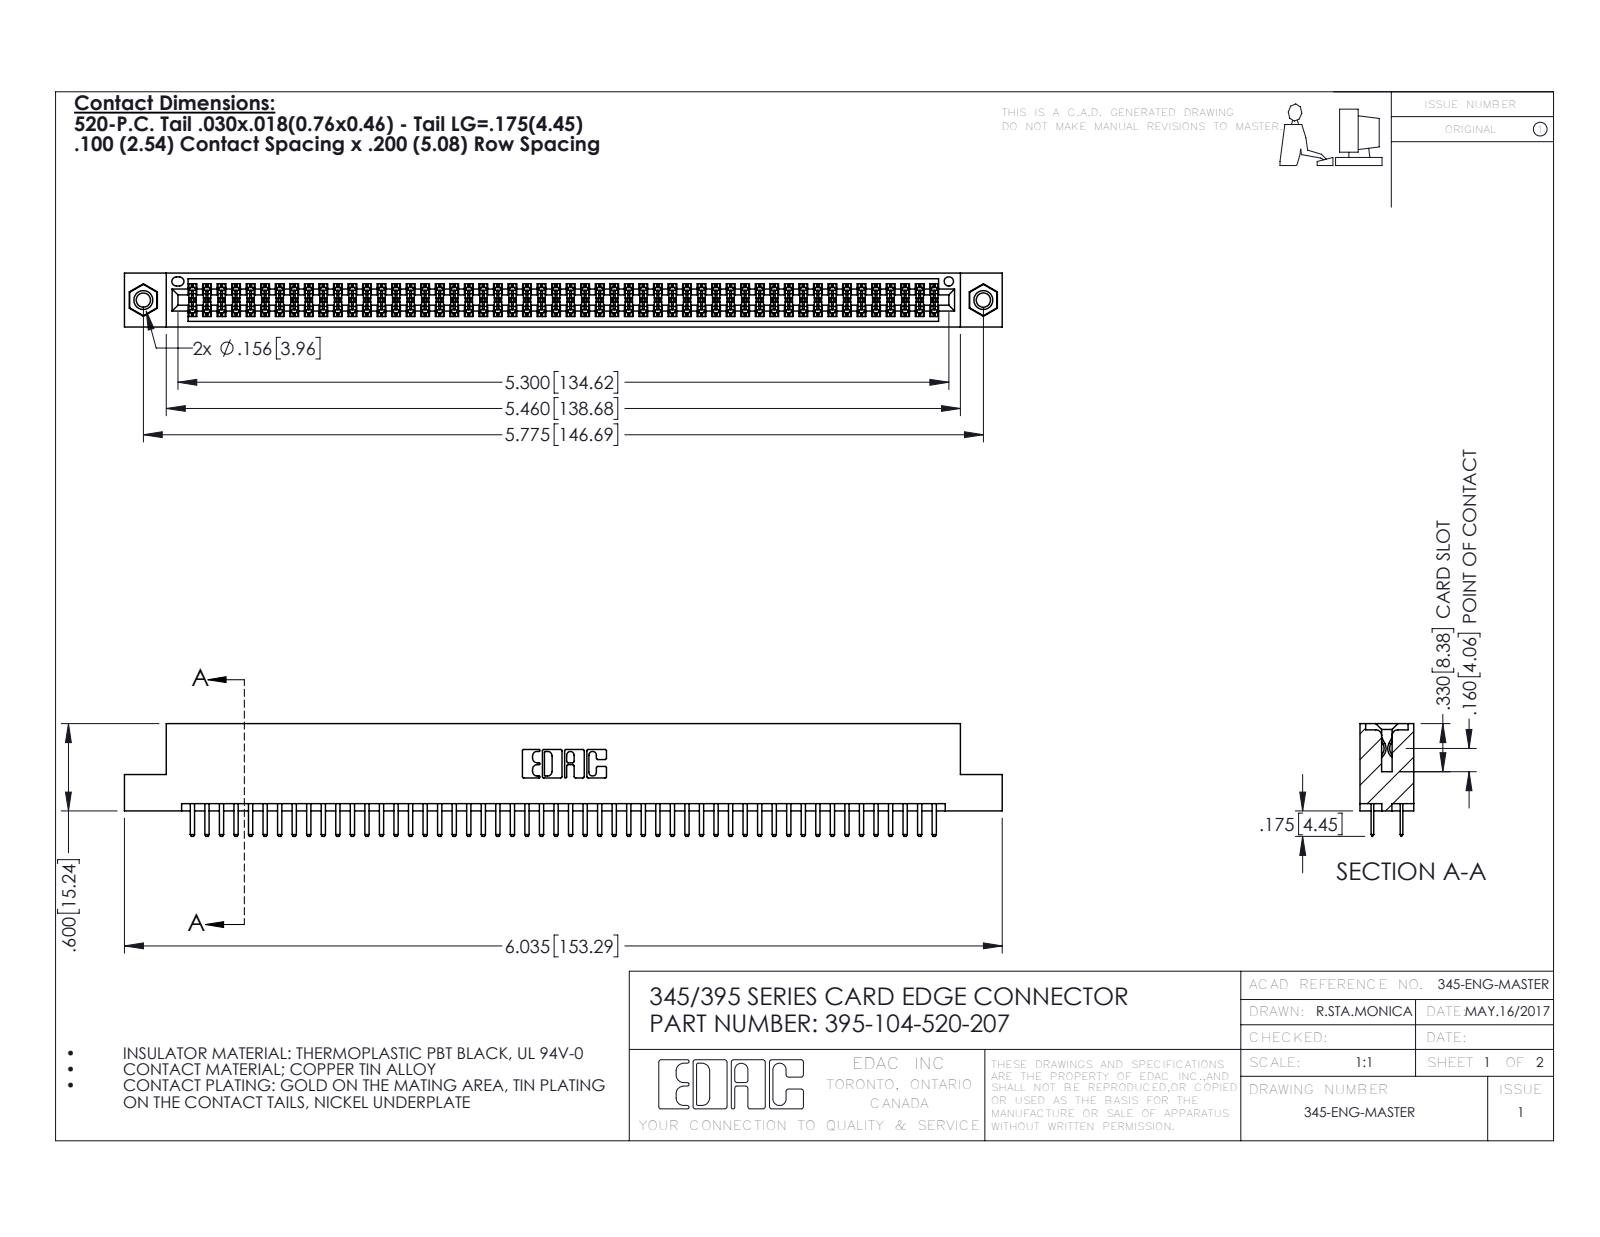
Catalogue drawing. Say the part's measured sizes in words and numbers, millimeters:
The part is named "345-292-001_345-293-120; 395-104-520-207; 345-250-001_345-250-005-103; 345 Part_Flush Mounting Lugs - 0.156 Dia-TI". Its 3-D file was written by "SolidWorks 2016 (CONFIG_CONTROL_DESIGN)". It is 107 solids with 5802 faces: 3752 planar, 2034 cylindrical and 16 other. Overall it measures 153.3 by 19.7 by 9.4 millimeters. Its volume is 14 900 cubic millimeters and its surface area 22 190 square millimeters. Round holes: 2 of diameter 2.5, 2 of diameter 3.2, 2 of diameter 4, 1 of diameter 1.6. Round bosses or shafts: 2 of diameter 3.9. Partial cylindrical surfaces (rounded edges, fillets, slot ends): 156 of radius 0.2, 108 of radius 0.3, 22 of radius 0.3, 6 of radius 0.2, 6 of radius 0.8, 3 of radius 0.7, 2 of radius 0.4, 2 of radius 0.5. The main face-to-face distances are 1.8, 7.6, 5.1, 9.4, 2.5, 6.9, 0.6, 5.7, 0.6, 1.8. The hole center spacings are 6.9, 140.7, 146.7.
